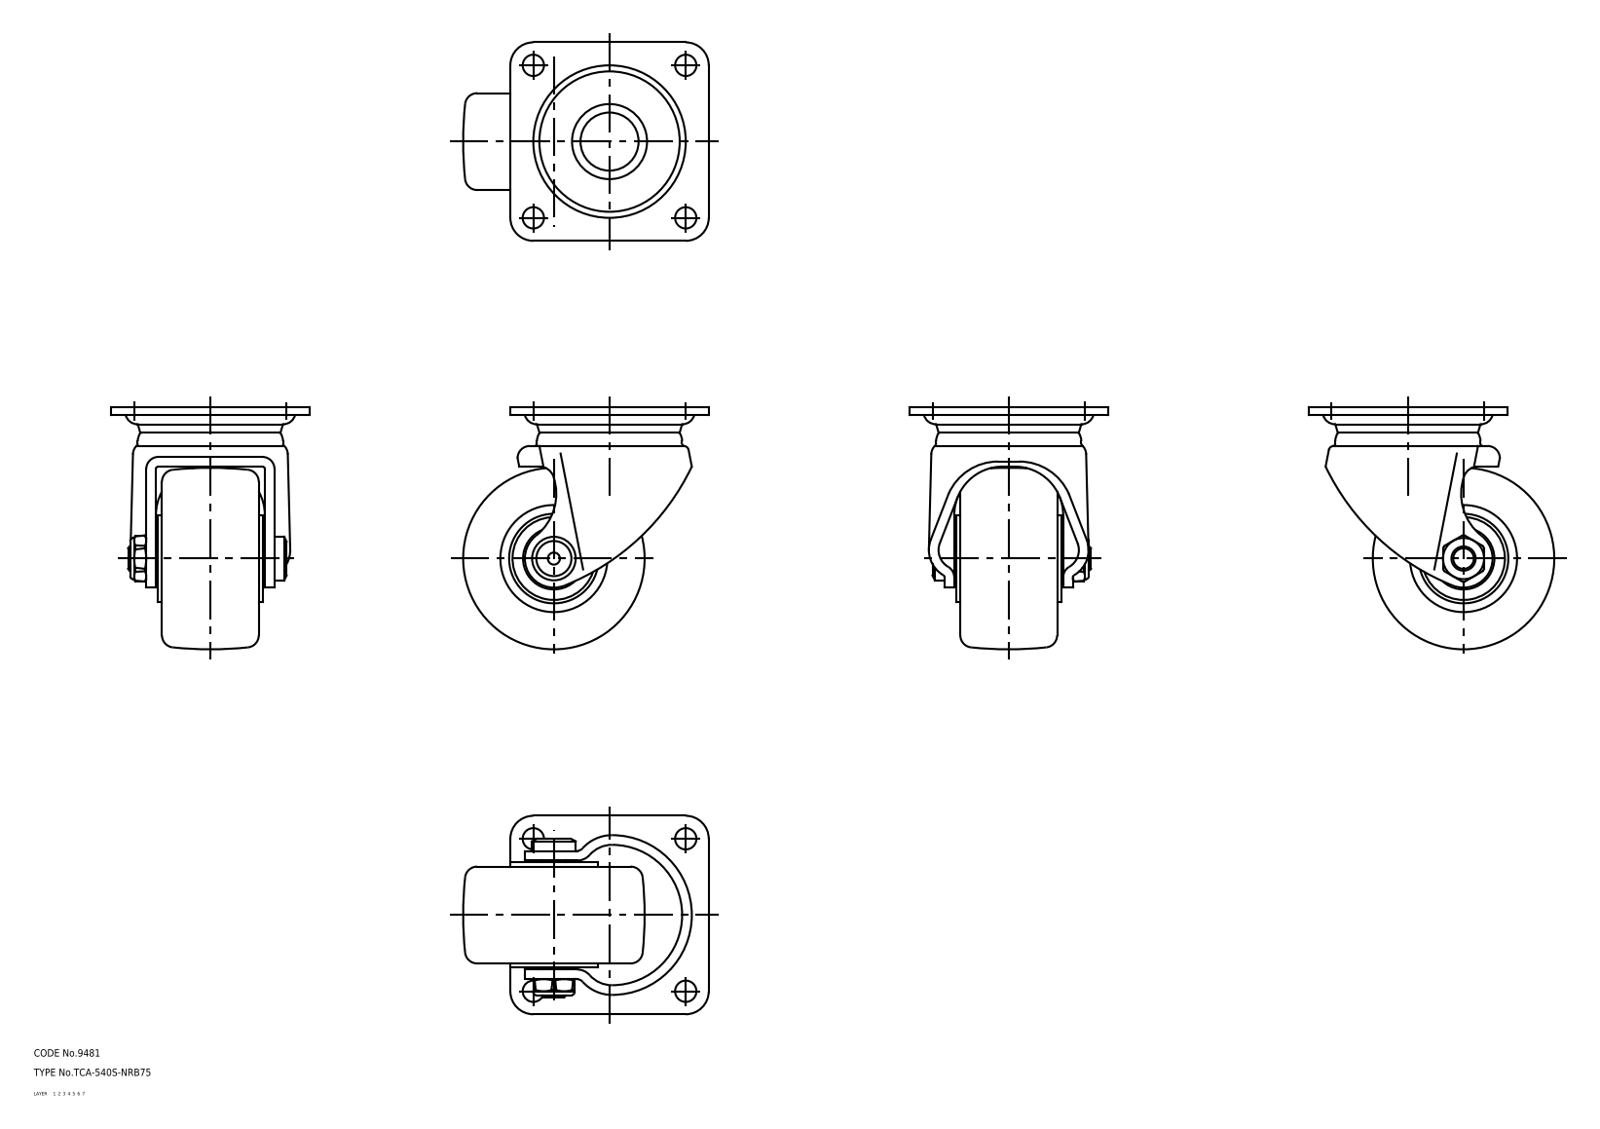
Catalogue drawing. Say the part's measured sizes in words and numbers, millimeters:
The part is named "main shaft; wheel; mounting plate; axle (+1 more)". Its 3-D file was written by "CADfix (AUTOMOTIVE_DESIGN)". It is 5 solids with 222 faces: 0 planar, 0 cylindrical and 222 other. Overall it measures 101.5 by 100 by 82 millimeters. Its volume is 270 548 cubic millimeters and its surface area 62 034 square millimeters.
